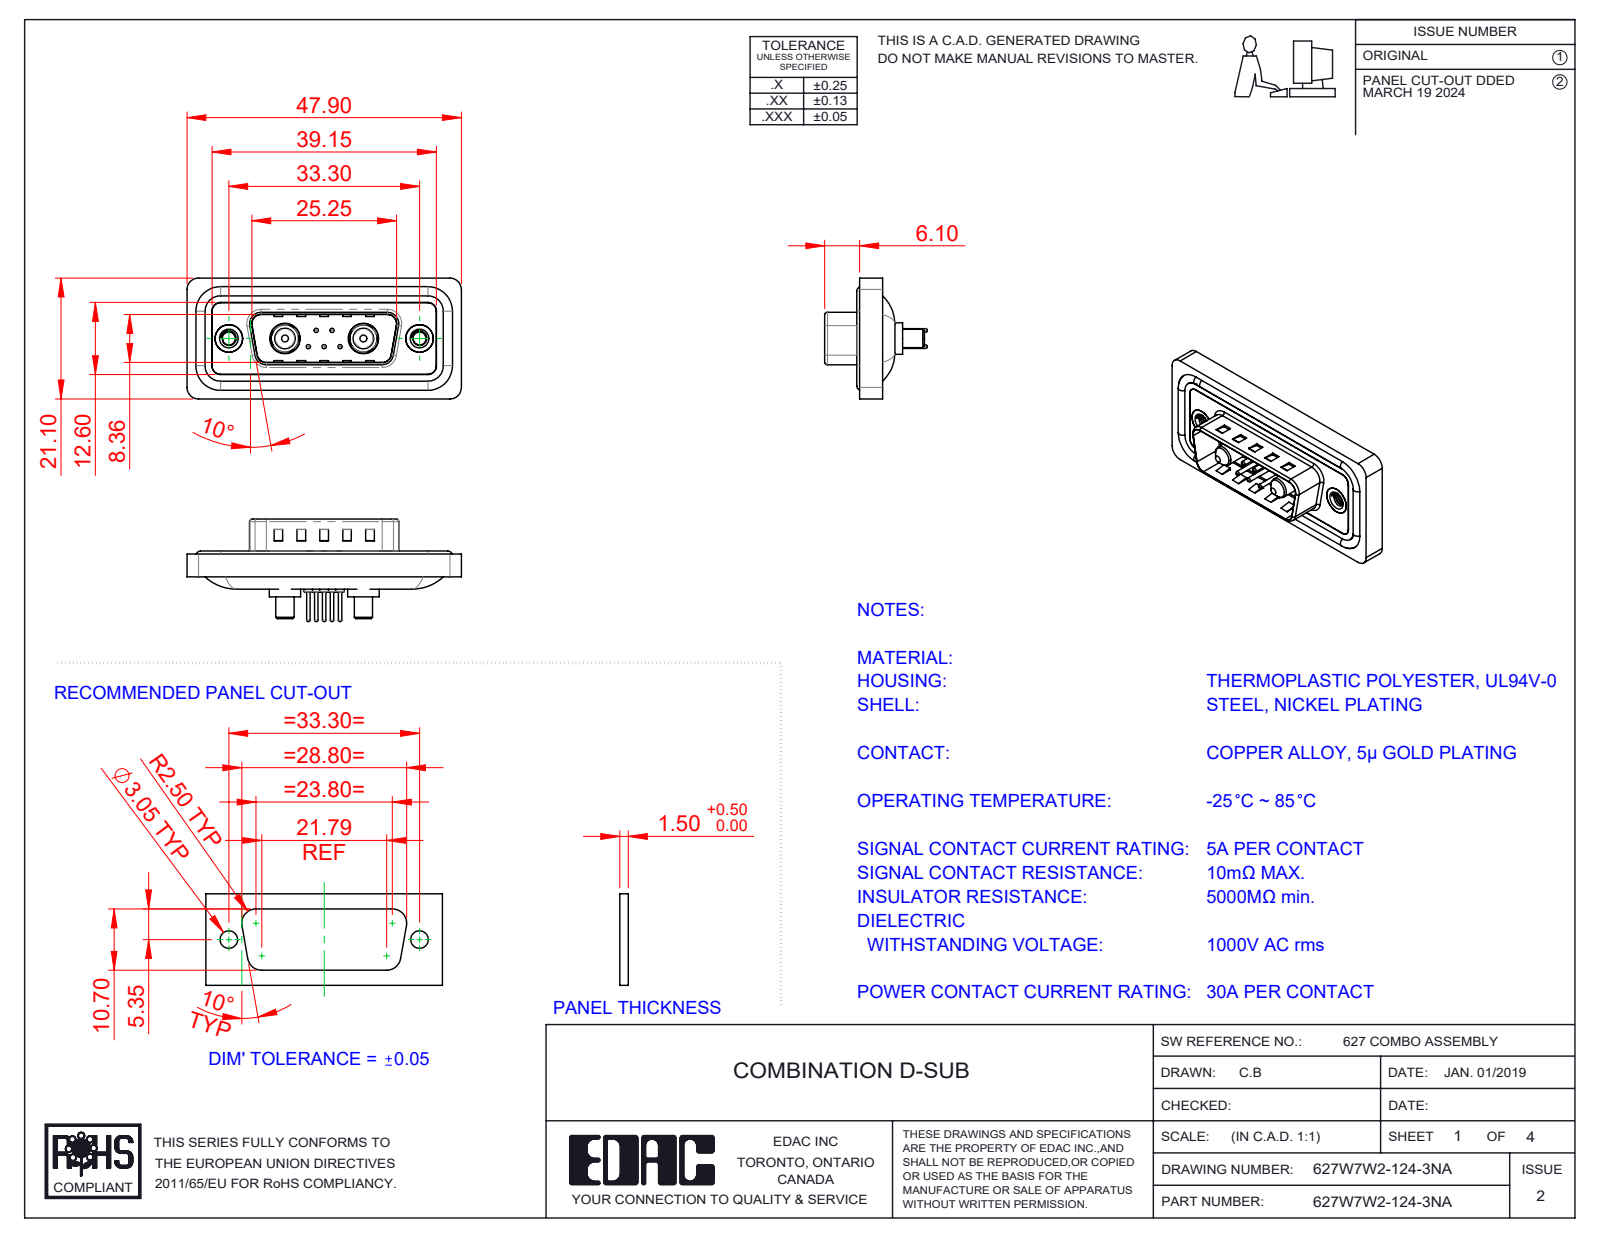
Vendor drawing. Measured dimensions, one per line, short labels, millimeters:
name: 627Combo Waterproof Housing_15 Contacts; 627Combo Threaded Rivet_A; 627Combo Shell Front_15 Contacts; 627Combo Shell Rear_15 Contacts (+5 more)
written by: SolidWorks 2023 (CONFIG_CONTROL_DESIGN)
unit: mm
bodies: 16 solids, 708 faces (232 planar, 294 cylindrical, 182 other)
size: 47.9 × 21.1 × 17.9
volume: 5 533 mm³; area: 8 800 mm²
holes: 5× ⌀0.75, 5× ⌀1.6, 5× ⌀2, 2× ⌀2.26, 2× ⌀4, 2× ⌀4.8, 2× ⌀4.85, 2× ⌀5, 2× ⌀5.3
bosses: 5× ⌀1.5, 5× ⌀0.6, 4× ⌀1.6, 2× ⌀5.5, 2× ⌀5.2, 2× ⌀4.9, 2× ⌀4.75, 2× ⌀3.75
rounds: 26× R1.5, 20× R2, 8× R0.5, 8× R1.6, 4× R0.25, 4× R0.6, 4× R0.65, 4× R0.9
face distances: 0.4, 1.1, 1.5, 1.6, 0.5, 3.1, 2.9, 0.82, 9.58, 2.5
hole spacings: 3.16, 2.77, 9.8, 23.5, 4.31, 4.33, 5.03, 5.04
